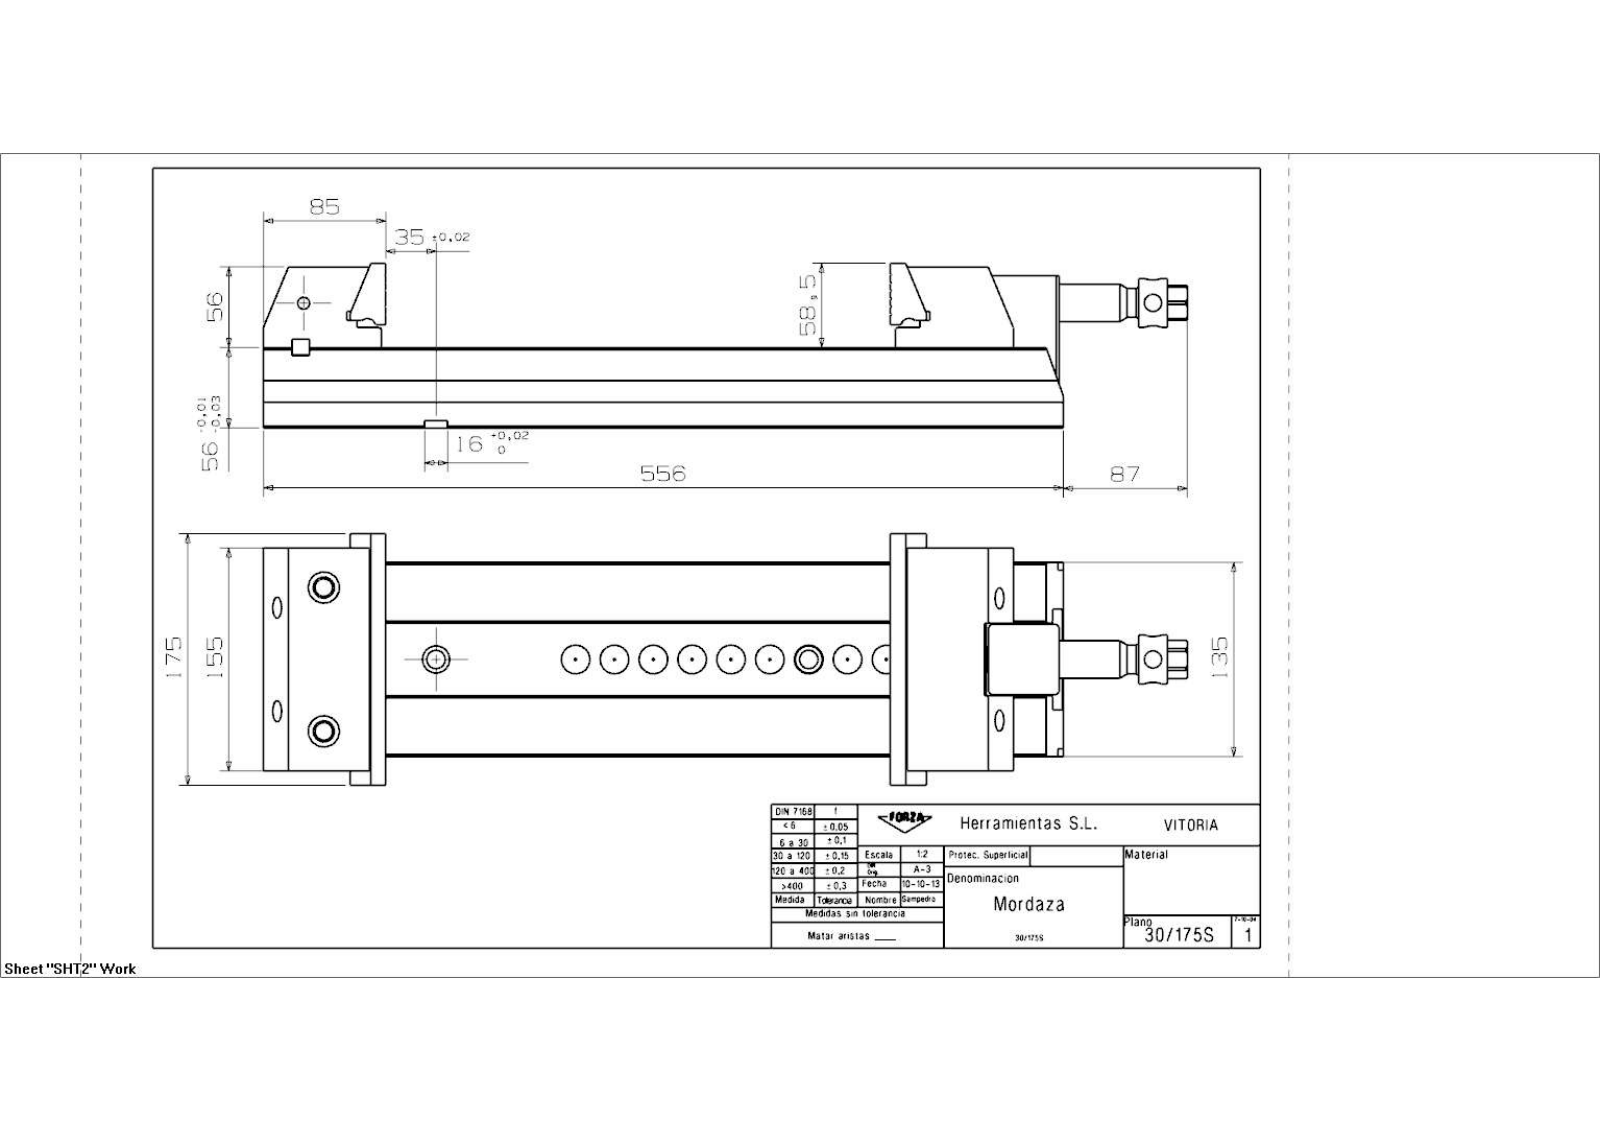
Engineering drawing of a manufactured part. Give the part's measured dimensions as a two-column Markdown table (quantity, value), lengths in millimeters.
| quantity | value |
| --- | --- |
| part name | 30_175S_Mordaza |
| STEP written by | SIEMENS PLM Software NX 7.5 (CONFIG_CONTROL_DESIGN) |
| units | millimeters |
| bodies | 12 solids, 465 faces (302 planar, 95 cylindrical, 68 other) |
| overall size | 642.23 × 175 × 114.5 |
| volume | 4 485 000 mm³ |
| surface area | 551 656 mm² |
| round holes (diameter × count) | 13 × 6, 15 × 6, 19 × 6, 5.19 × 5, 10 × 4, 10.58 × 4, 8.78 × 3, 6.99 × 2, 8.5 × 2, 12 × 2, 12.38 × 2, 22 × 2 |
| round bosses / shafts (diameter × count) | 34 × 1, 33.8 × 1, 26 × 1, 20 × 1, 16.5 × 1 |
| partial cylindrical surfaces (radius × count) | 8 × 4, 20 × 4, 1.6 × 2, 6 × 2, 7 × 2, 4 × 1, 9 × 1, 10.5 × 1 |
| main face-to-face distances | 56, 31.8, 24.2, 32.5, 102.5, 135, 27, 1, 10, 23.2 |
| hole center spacings | 6.5, 72, 78.5, 106.07, 27.76, 30, 34.21, 34.22 |
